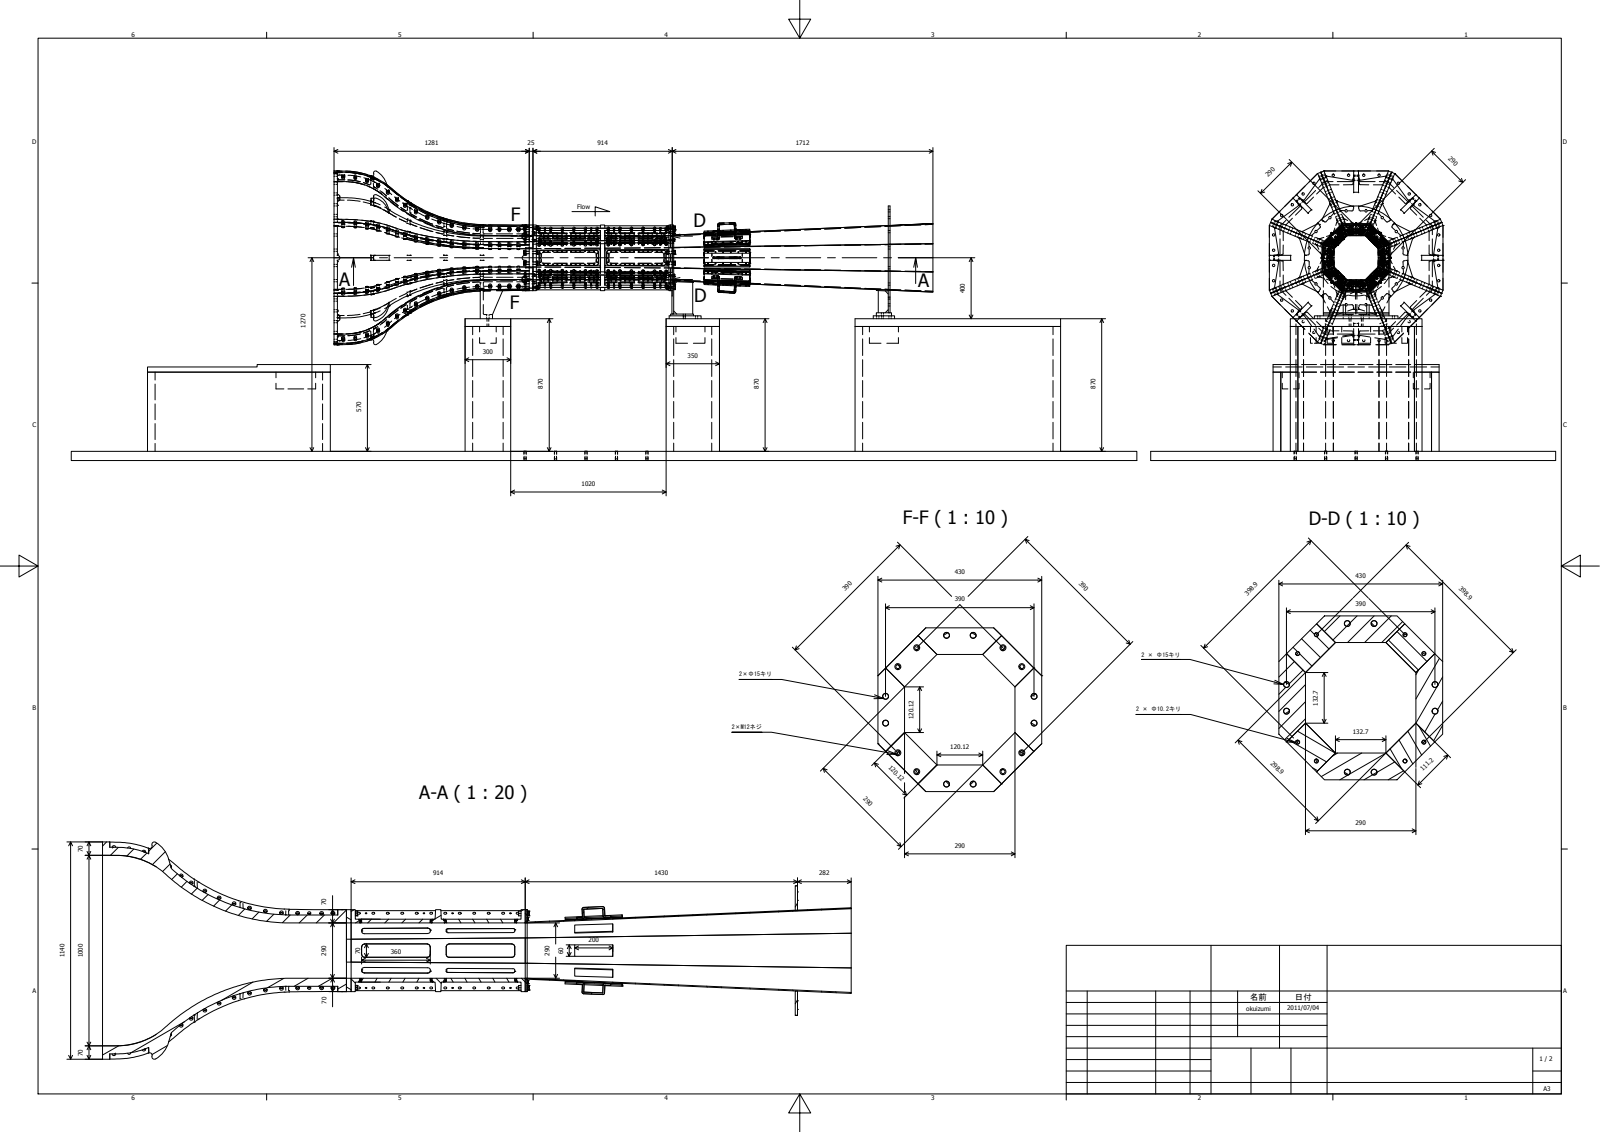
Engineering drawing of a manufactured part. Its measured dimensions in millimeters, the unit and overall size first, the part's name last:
Units: millimetres
Overall size (bounding box): 6995 × 4490 × 1900
Round holes (diameter × count): ⌀4.2 ×344, ⌀5.5 ×344, ⌀15 ×178, ⌀19 ×150, ⌀10.2 ×112, ⌀5 ×80, ⌀6 ×48, ⌀8 ×32, ⌀16 ×31, ⌀12 ×25, ⌀14 ×8, ⌀10.8 ×6
Round bosses / shafts (diameter × count): ⌀9 ×40, ⌀15 ×25, ⌀16 ×17, ⌀24 ×16, ⌀10 ×8
Partial cylindrical surfaces — rounded edges, fillets, slot ends (radius × count): R7 ×153, R15 ×144, R10 ×32, R13 ×16, R16 ×12, R150 ×8, R250 ×1, R340 ×1
Main face-to-face distances: 60, 50, 300, 350, 112.5, 927.5, 815, 4.5, 880, 820
Hole centre spacings: 150, 200, 50, 89.31, 30, 100, 60, 447.21
Volume: 2 603 000 000 mm³ · Surface area: 114 600 000 mm²
Bodies: 245 solids, 7758 faces (2440 planar, 2435 cylindrical, 2883 other)
Part name (STEP PRODUCT): 小型低乱調風洞（総組）; 測定部台座; 測定部台座A; 測定部台座A_01 (+8 more)
STEP written by: Autodesk Inventor 2011 (AUTOMOTIVE_DESIGN)
